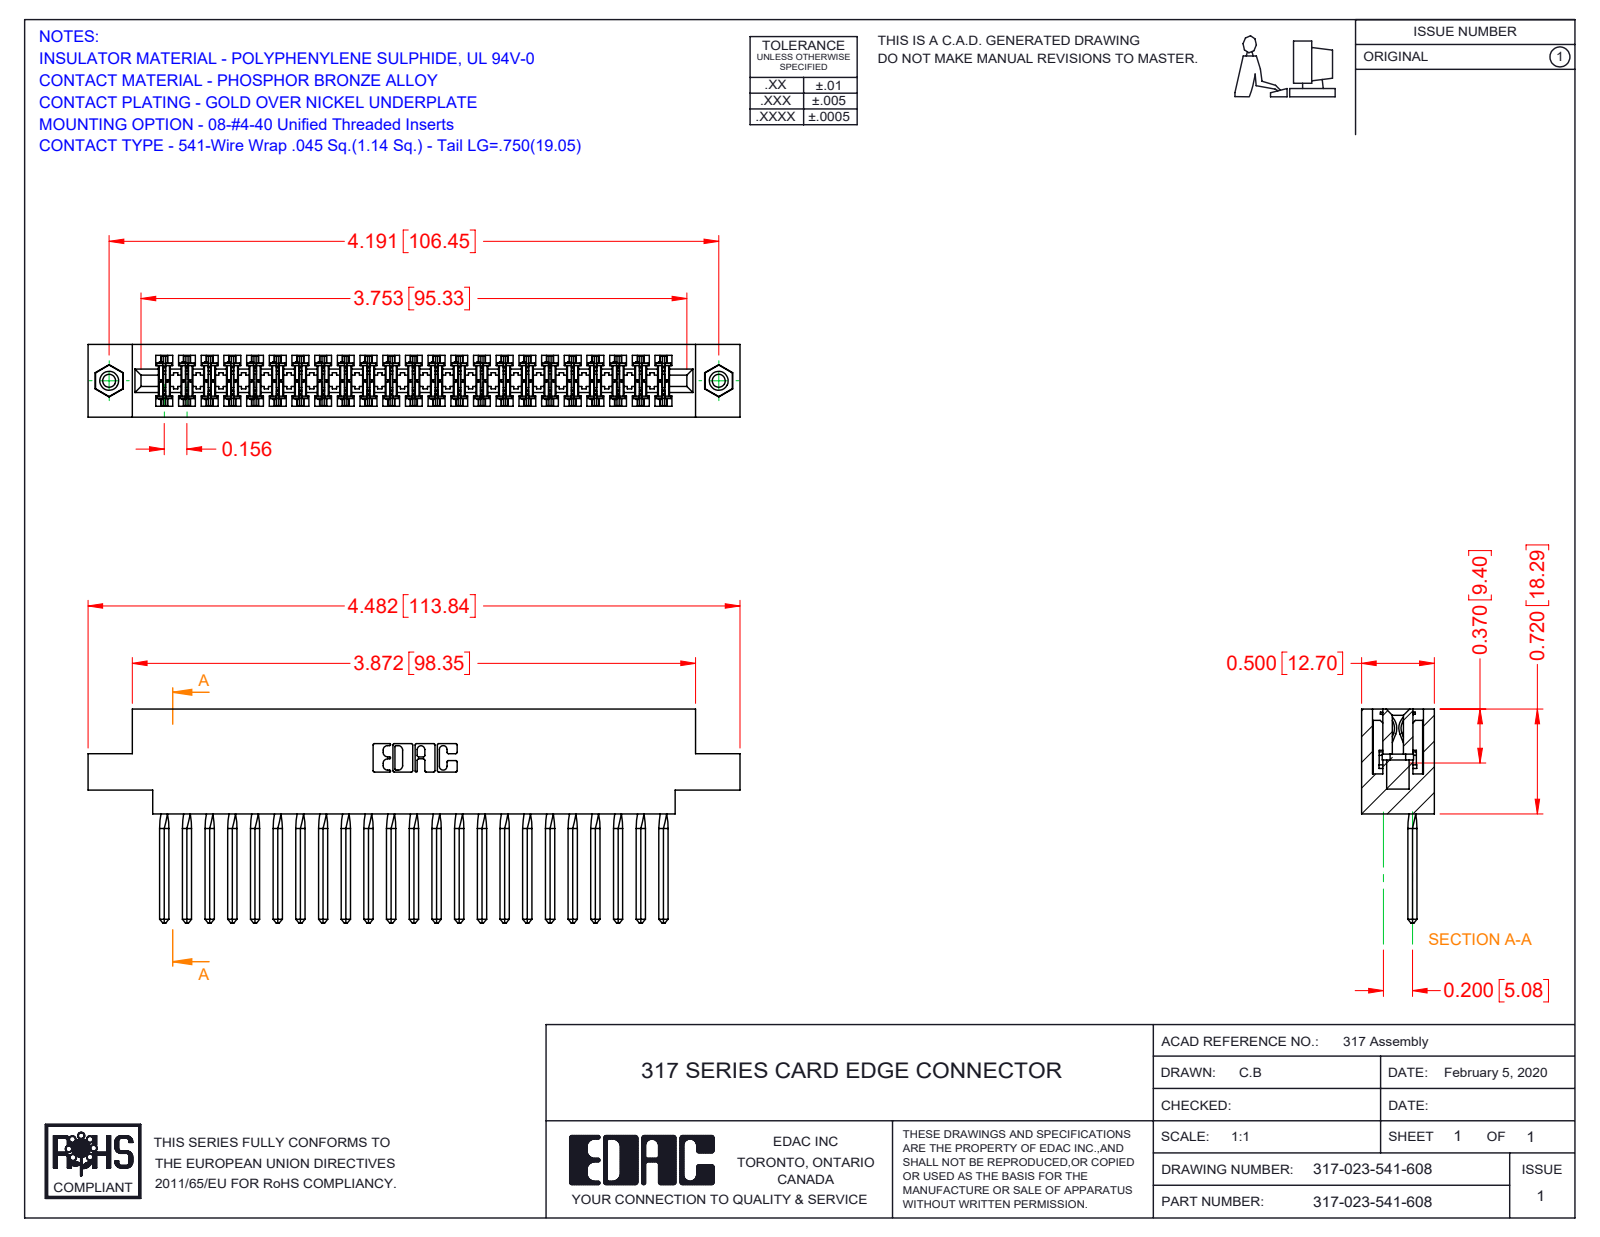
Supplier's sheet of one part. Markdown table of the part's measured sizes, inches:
| quantity | value |
| --- | --- |
| part name | 317-023-541-678; 317 Part_.156 Dia - TI; 317-290-002_541; 345-250-001_345-250-003-102 |
| STEP written by | SolidWorks 2016 (CONFIG_CONTROL_DESIGN) |
| units | inches |
| bodies | 26 solids, 3658 faces (2942 planar, 608 cylindrical, 108 other) |
| overall size | 4.482 × 1.47 × 0.5 |
| volume | 1.091 in³ |
| surface area | 38.19 in² |
| round holes (diameter × count) | 0.089 × 2, 0.125 × 2, 0.156 × 2 |
| round bosses / shafts (diameter × count) | 0.155 × 2 |
| partial cylindrical surfaces (radius × count) | 0.015 × 46, 0.01 × 22, 0.007 × 6, 0.031 × 6, 0.026 × 3, 0.095 × 2, 0.1 × 2, 0.11 × 2 |
| main face-to-face distances | 0.5, 0.075, 0.425, 0.11, 0.35, 0.195, 0.772, 0.22, 0.72, 0.136 |
| hole center spacings | 4.191 |
